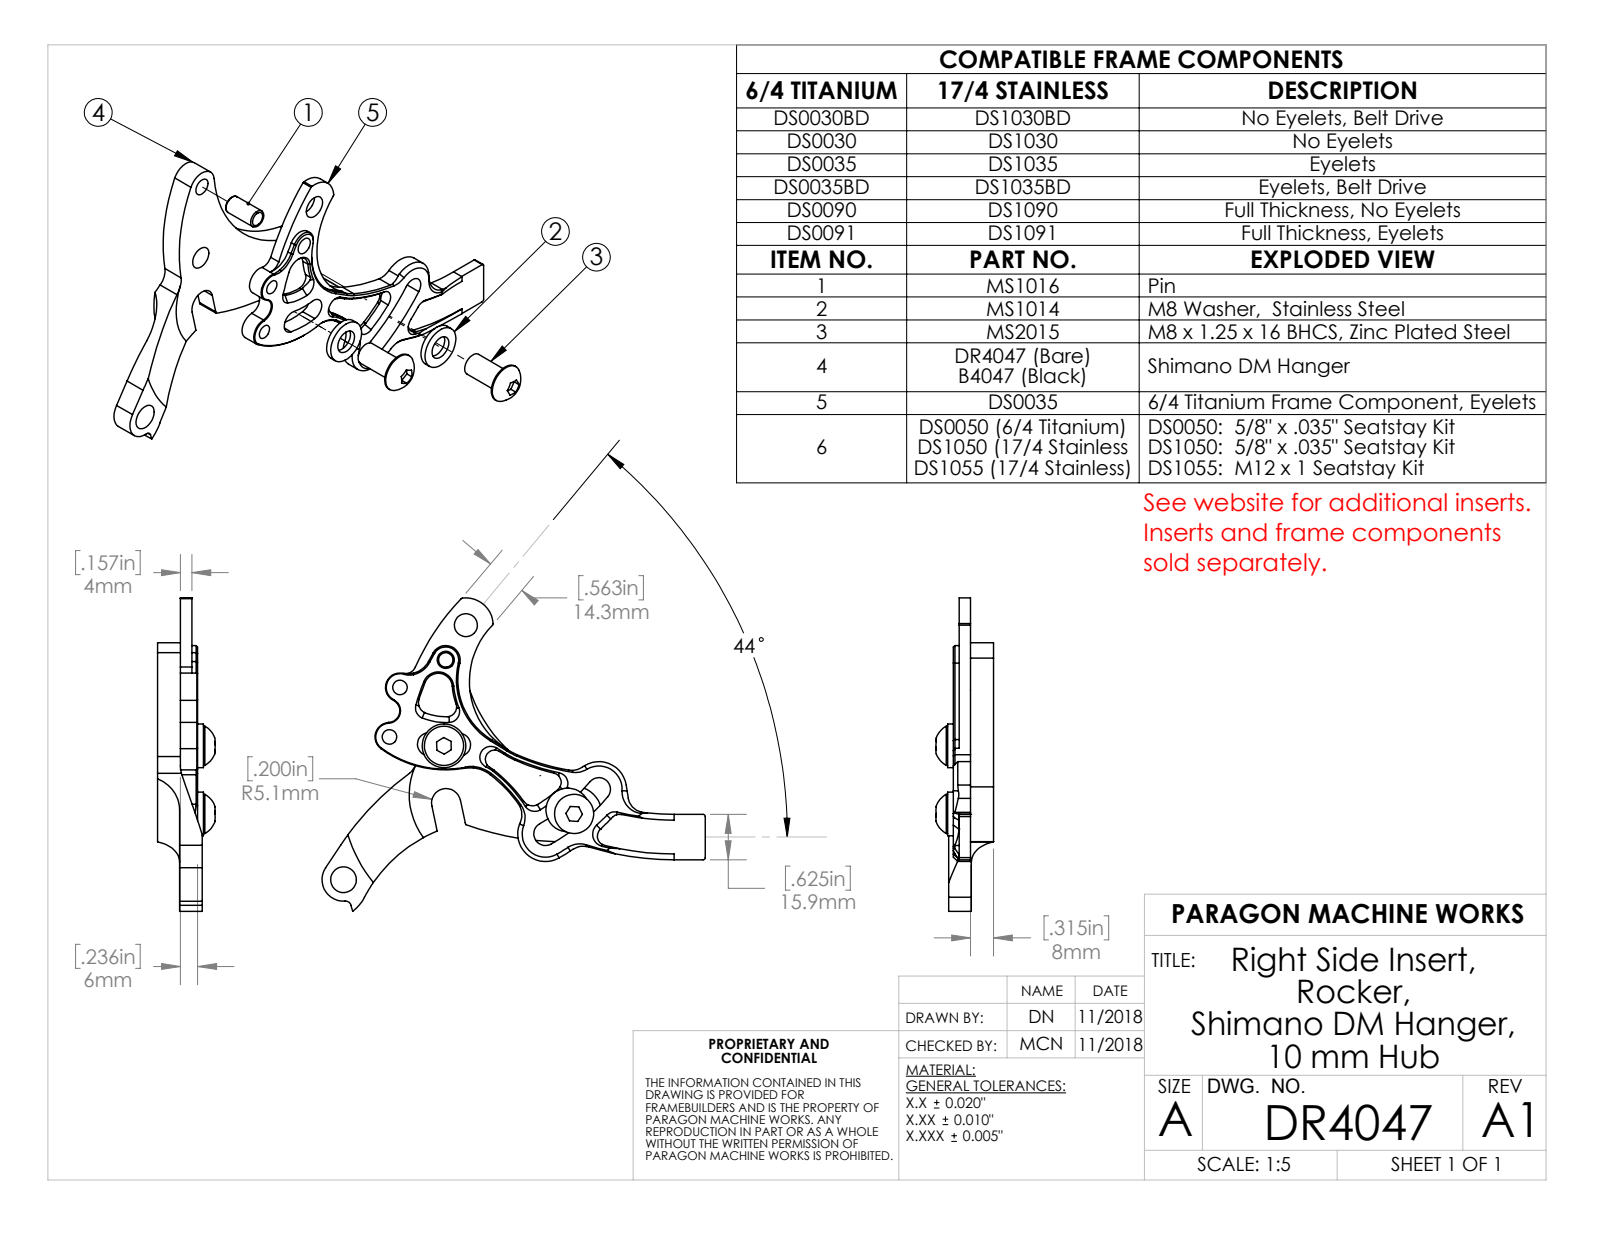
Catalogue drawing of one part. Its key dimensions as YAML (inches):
part_name: "DR4047"
step_written_by: "SolidWorks 2018 (AUTOMOTIVE_DESIGN)"
units: inches
bodies: {solids: 1, faces: 35, planar: 8, cylindrical: 24, other: 3}
overall_size: [3.826, 3.717, 0.615]
volume: 1.31
surface_area: 13.98
round_holes:
  - {diameter: 0.315, count: 2}
  - {diameter: 0.236, count: 1}
  - {diameter: 0.354, count: 1}
partial_cylinders:
  - {radius: 0.079, count: 1}
  - {radius: 0.1, count: 1}
  - {radius: 0.2, count: 1}
  - {radius: 0.236, count: 1}
  - {radius: 0.236, count: 1}
  - {radius: 0.295, count: 1}
  - {radius: 0.38, count: 1}
  - {radius: 0.591, count: 1}
face_to_face_distances: [0.315, 0.304, 0.615, 0.311, 0.3, 0.4]
hole_center_spacings: [1.181, 2.019, 2.301, 2.756, 3.297, 3.331]
